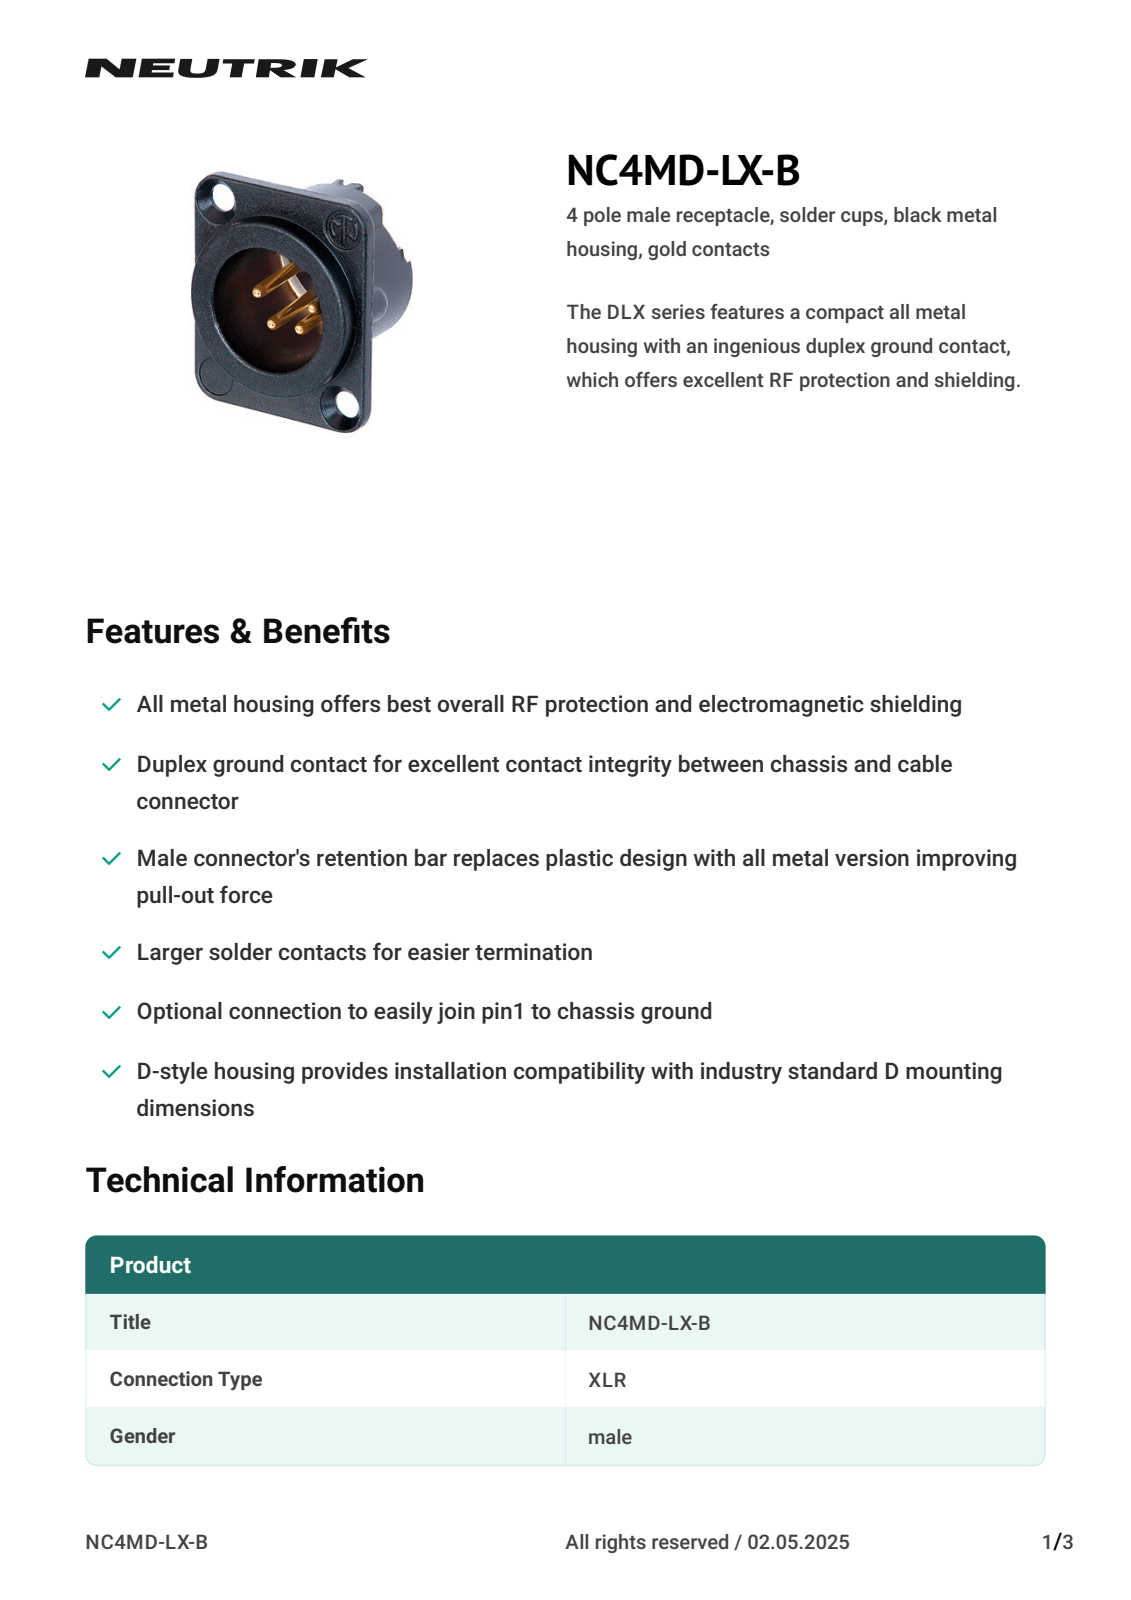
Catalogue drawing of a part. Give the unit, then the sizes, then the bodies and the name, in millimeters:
Units: millimetres
Overall size (bounding box): 31 × 26 × 25.4
Round holes (diameter × count): ⌀1.7 ×4, ⌀3.5 ×2, ⌀5 ×2, ⌀6 ×2, ⌀1.6 ×1
Round bosses / shafts (diameter × count): ⌀2.3 ×4, ⌀1.59 ×4, ⌀23.6 ×1
Partial cylindrical surfaces — rounded edges, fillets, slot ends (radius × count): R0.3 ×20, R0.2 ×12, R0.25 ×9, R1 ×5, R0.45 ×4, R0.5 ×4, R1.15 ×4, R3.5 ×4
Main face-to-face distances: 2, 4.7, 2.7, 18.25, 13.55, 15.55, 18.3, 3.35, 16.3, 14.9
Hole centre spacings: 4.27, 13.12, 18.2, 19, 24, 30.61, 4.24, 6.93
Volume: 4 167 mm³ · Surface area: 4 662 mm²
Bodies: 1 solid, 959 faces (692 planar, 138 cylindrical, 129 other)
Part name (STEP PRODUCT): NC4MD-LX-B
STEP written by: CREO PARAMETRIC BY PTC INC, 2021184 (AUTOMOTIVE_DESIGN)
